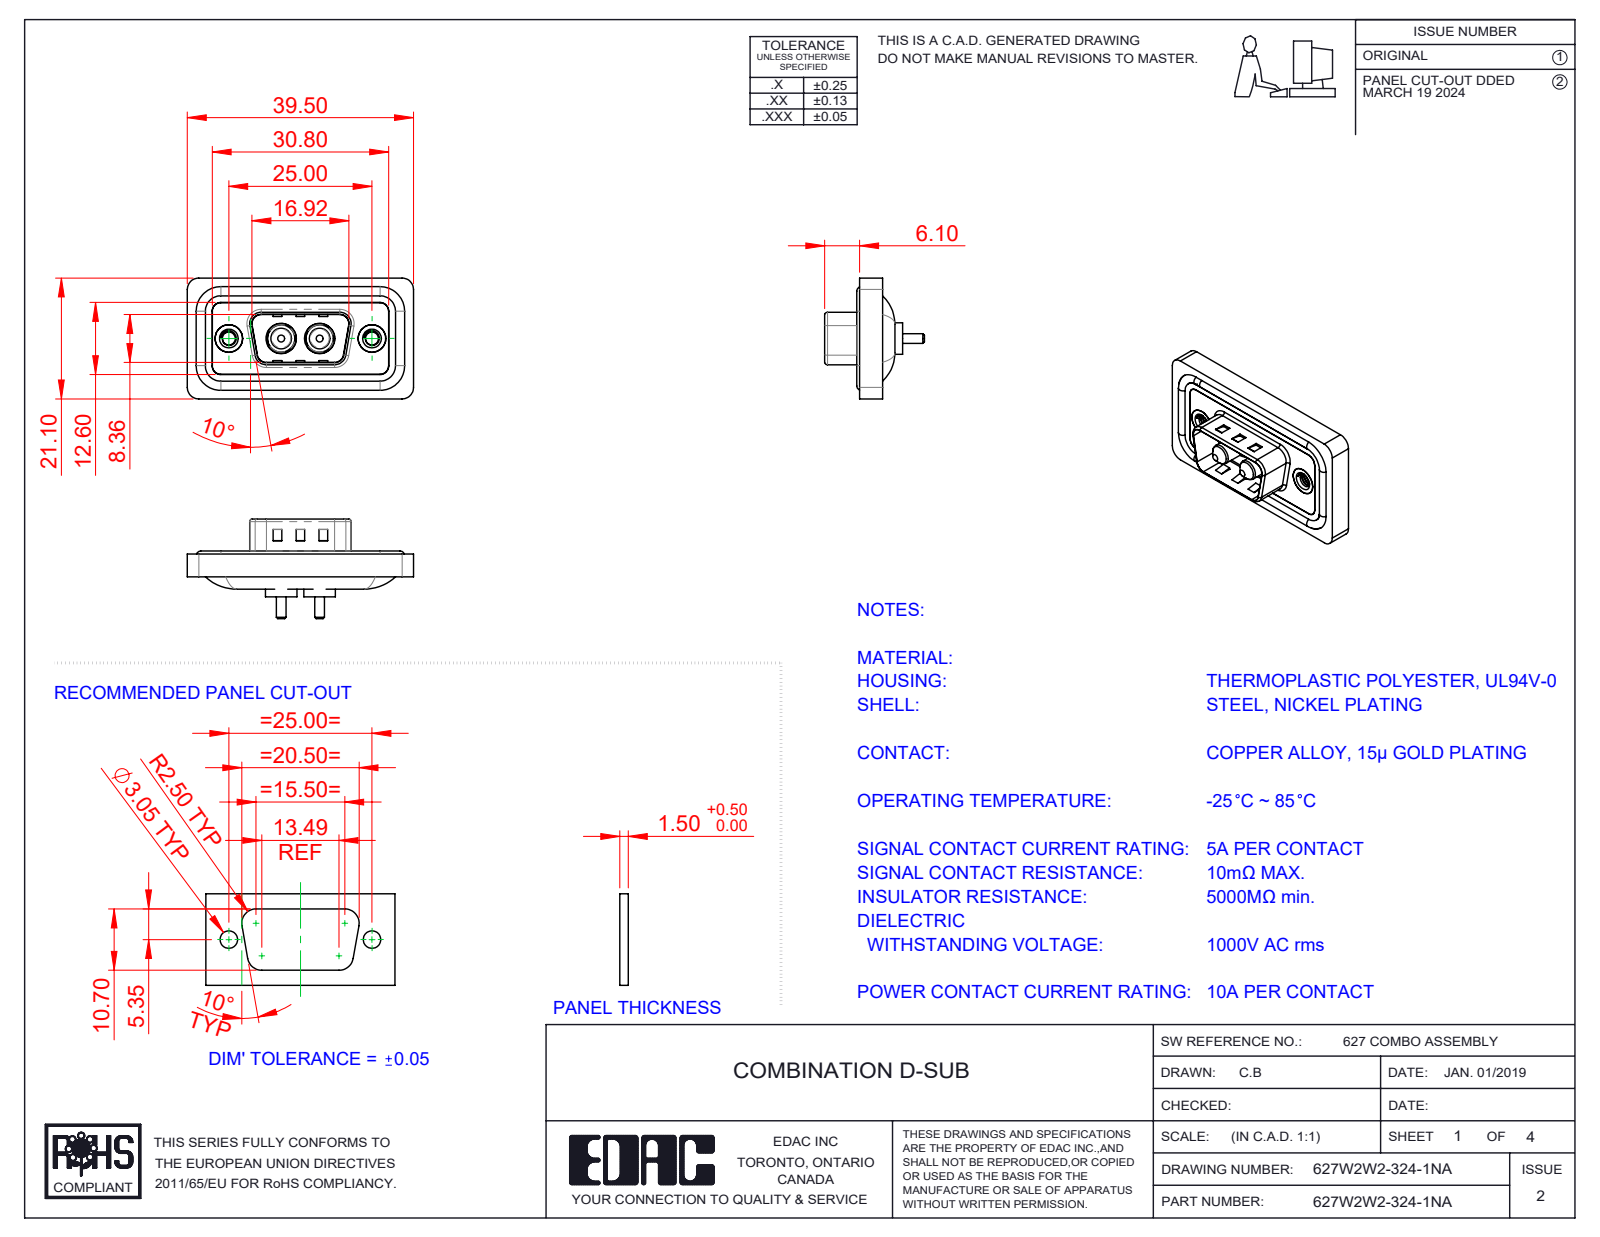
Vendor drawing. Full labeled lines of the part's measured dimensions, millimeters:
Part name (STEP PRODUCT): 627W2W2-324-1NA; 627Combo Housing_2W2; 627Combo Shell Front_09 Contacts; 627Combo Threaded Rivet_A (+3 more)
STEP written by: SolidWorks 2023 (CONFIG_CONTROL_DESIGN)
Units: millimetres
Bodies: 11 solids, 487 faces (165 planar, 220 cylindrical, 102 other)
Overall size (bounding box): 39.5 × 21.1 × 17.4
Volume: 4 433 mm³ · Surface area: 6 956 mm²
Round holes (diameter × count): ⌀2.26 ×2, ⌀4 ×2, ⌀4.8 ×2, ⌀4.85 ×2, ⌀5 ×2, ⌀5.3 ×2
Round bosses / shafts (diameter × count): ⌀1.6 ×4, ⌀5.5 ×2, ⌀5.2 ×2, ⌀4.9 ×2, ⌀4.75 ×2, ⌀3.75 ×2, ⌀3.6 ×2, ⌀1.7 ×2
Partial cylindrical surfaces — rounded edges, fillets, slot ends (radius × count): R1.5 ×22, R2 ×18, R0.5 ×8, R1.6 ×8, R0.25 ×4, R0.6 ×4, R0.65 ×4, R0.9 ×4
Main face-to-face distances: 0.4, 1.1, 2.9, 3.1, 0.5, 1.5, 1.6, 4, 2.5, 0.7
Hole centre spacings: 9.14, 15.86, 6.72, 25
